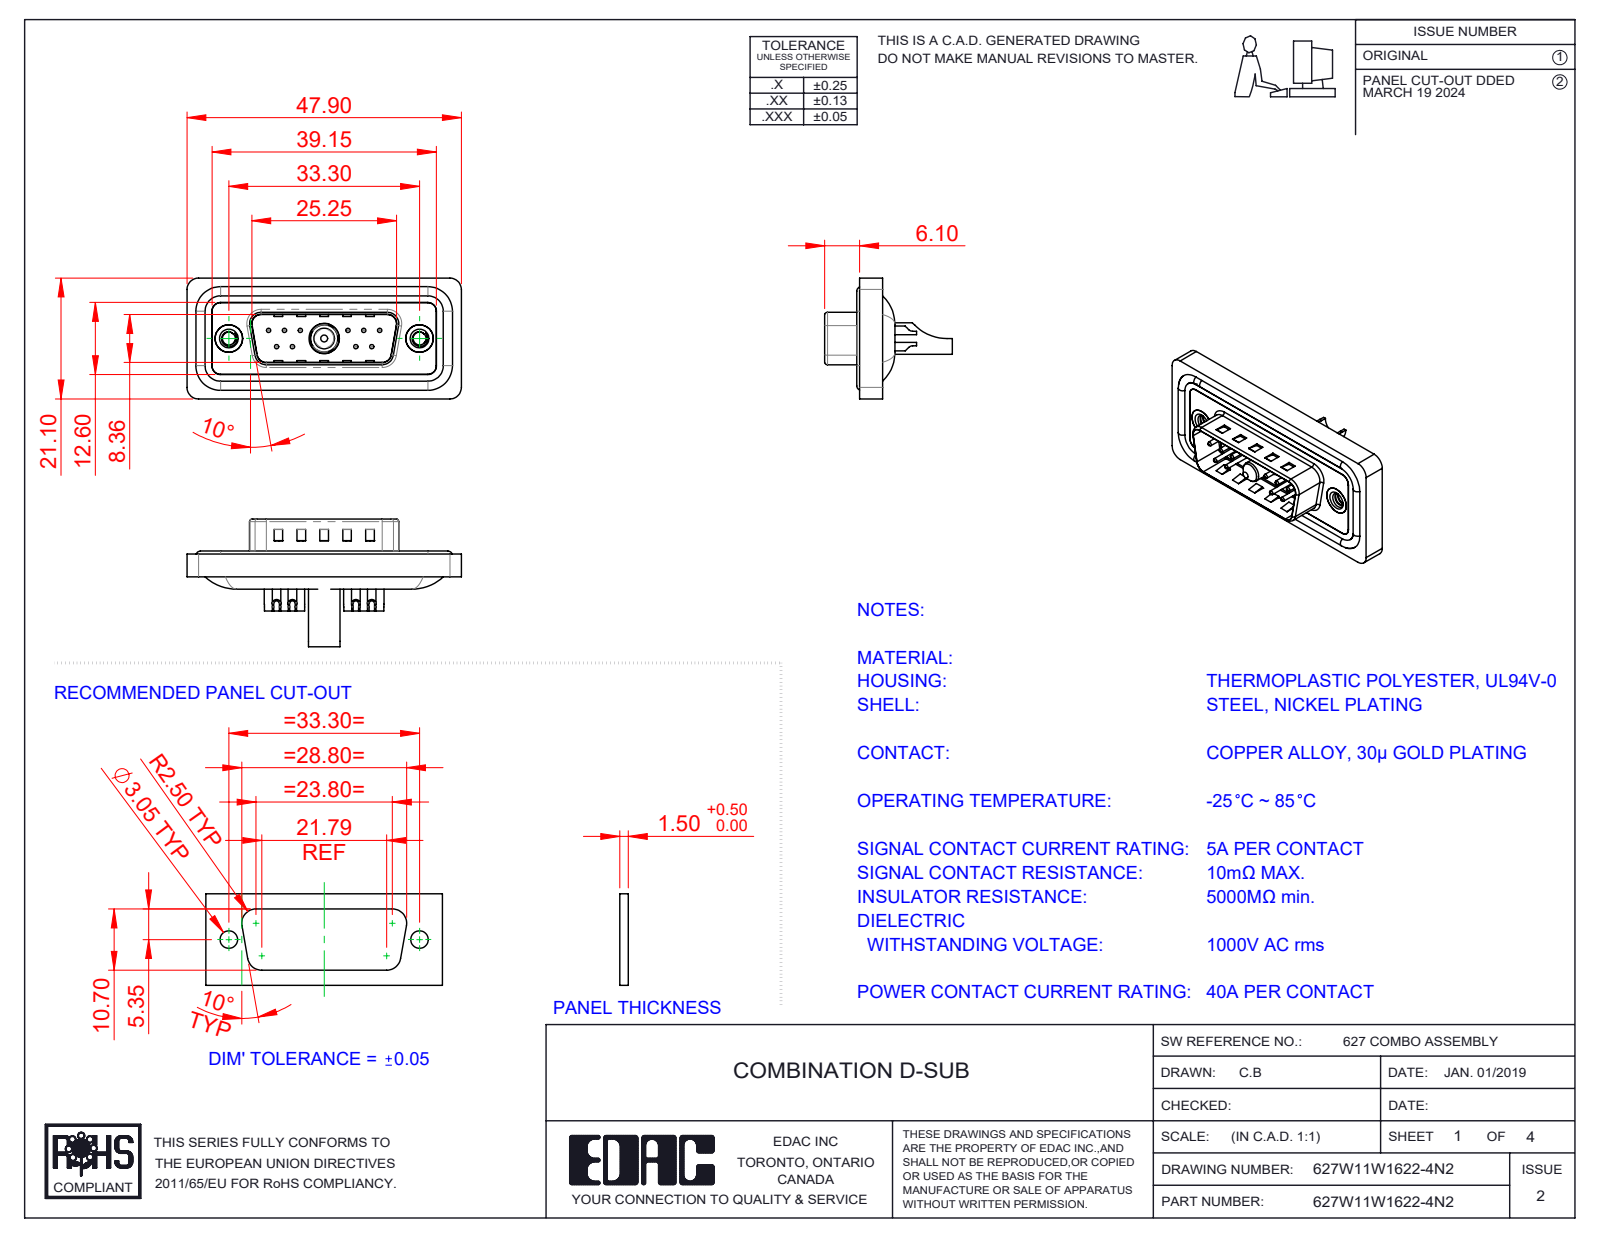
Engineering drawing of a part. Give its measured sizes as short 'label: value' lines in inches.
name: 627Combo Shell Front_15 Contacts; 627Combo Contact Row 1_22; 627Combo Housing_11W1; 627Combo Contact Row 2_22 (+5 more)
written by: SolidWorks 2023 (CONFIG_CONTROL_DESIGN)
unit: in
bodies: 19 solids, 873 faces (288 planar, 368 cylindrical, 217 other)
size: 1.886 × 0.878 × 0.831
volume: 0.336 in³; area: 14.04 in²
holes: 10× ⌀0.03, 10× ⌀0.039, 10× ⌀0.063, 10× ⌀0.079, 2× ⌀0.089, 2× ⌀0.157, 2× ⌀0.189, 2× ⌀0.197, 1× ⌀0.181, 1× ⌀0.191, 1× ⌀0.209
bosses: 10× ⌀0.059, 4× ⌀0.063, 2× ⌀0.193, 1× ⌀0.217, 1× ⌀0.205, 1× ⌀0.187, 1× ⌀0.148, 1× ⌀0.142
rounds: 26× R0.059, 20× R0.079, 9× R0.039, 8× R0.02, 8× R0.063, 4× R0.01, 4× R0.024, 4× R0.026
face distances: 0.016, 0.043, 0.063, 0.059, 0.02, 0.114, 0.122, 0.098, 0.161, 0.032
hole spacings: 0.124, 0.109, 0.545, 0.436, 0.654, 0.198, 0.198, 0.218
